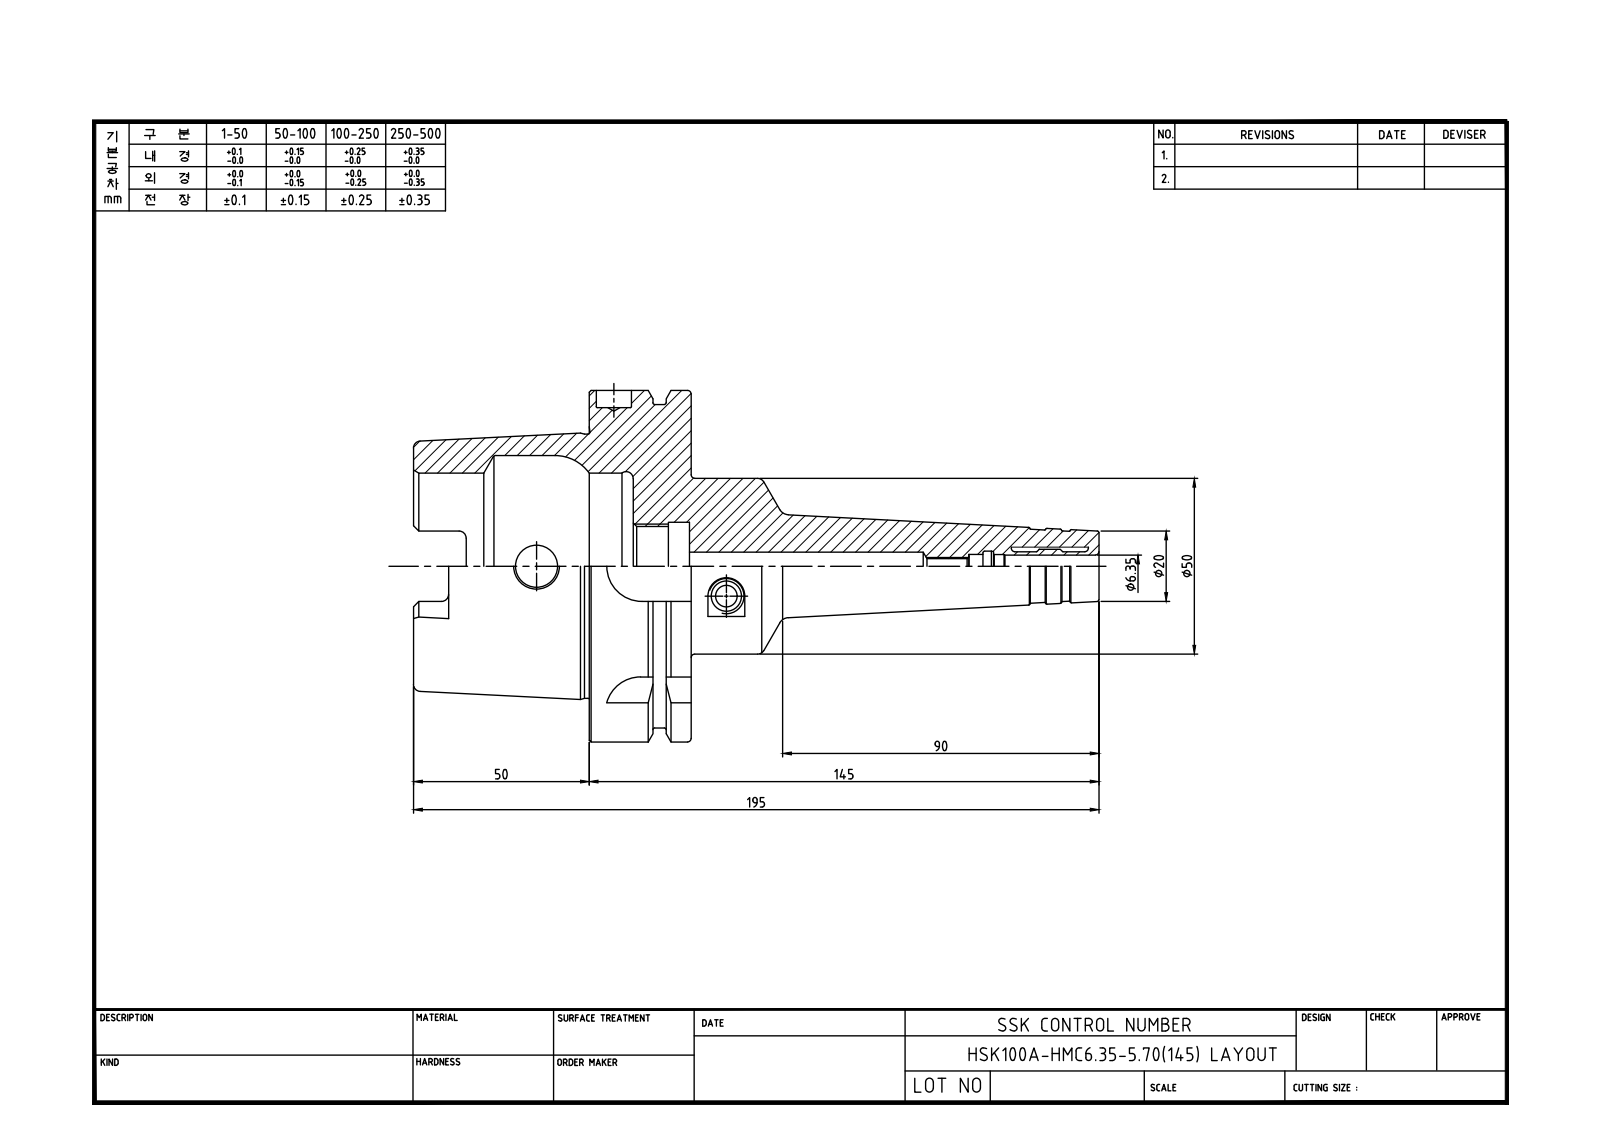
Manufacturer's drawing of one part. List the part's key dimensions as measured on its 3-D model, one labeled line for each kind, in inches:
Part name (STEP PRODUCT): HSK100A-HMC6.35-145
STEP written by: Autodesk Inventor 2020 (AUTOMOTIVE_DESIGN)
Units: inches
Bodies: 1 solid, 134 faces (38 planar, 35 cylindrical, 61 other)
Overall size (bounding box): 7.677 × 3.937 × 3.937
Volume: 20.75 in³ · Surface area: 96.29 in²
Round holes (diameter × count): ⌀0.169 ×1, ⌀0.25 ×1, ⌀0.268 ×1, ⌀0.315 ×1, ⌀0.394 ×1, ⌀0.472 ×1, ⌀0.881 ×1, ⌀0.984 ×1, ⌀2.087 ×1, ⌀2.48 ×1
Round bosses / shafts (diameter × count): ⌀3.937 ×1, ⌀3.622 ×1, ⌀2.969 ×1, ⌀1.969 ×1
Partial cylindrical surfaces — rounded edges, fillets, slot ends (radius × count): R0.079 ×6, R0.192 ×4, R0.394 ×4
Main face-to-face distances: 1.142, 0.492, 0.65, 2.461, 3.11, 1.969, 3.091, 1.122, 0.63, 0.02
